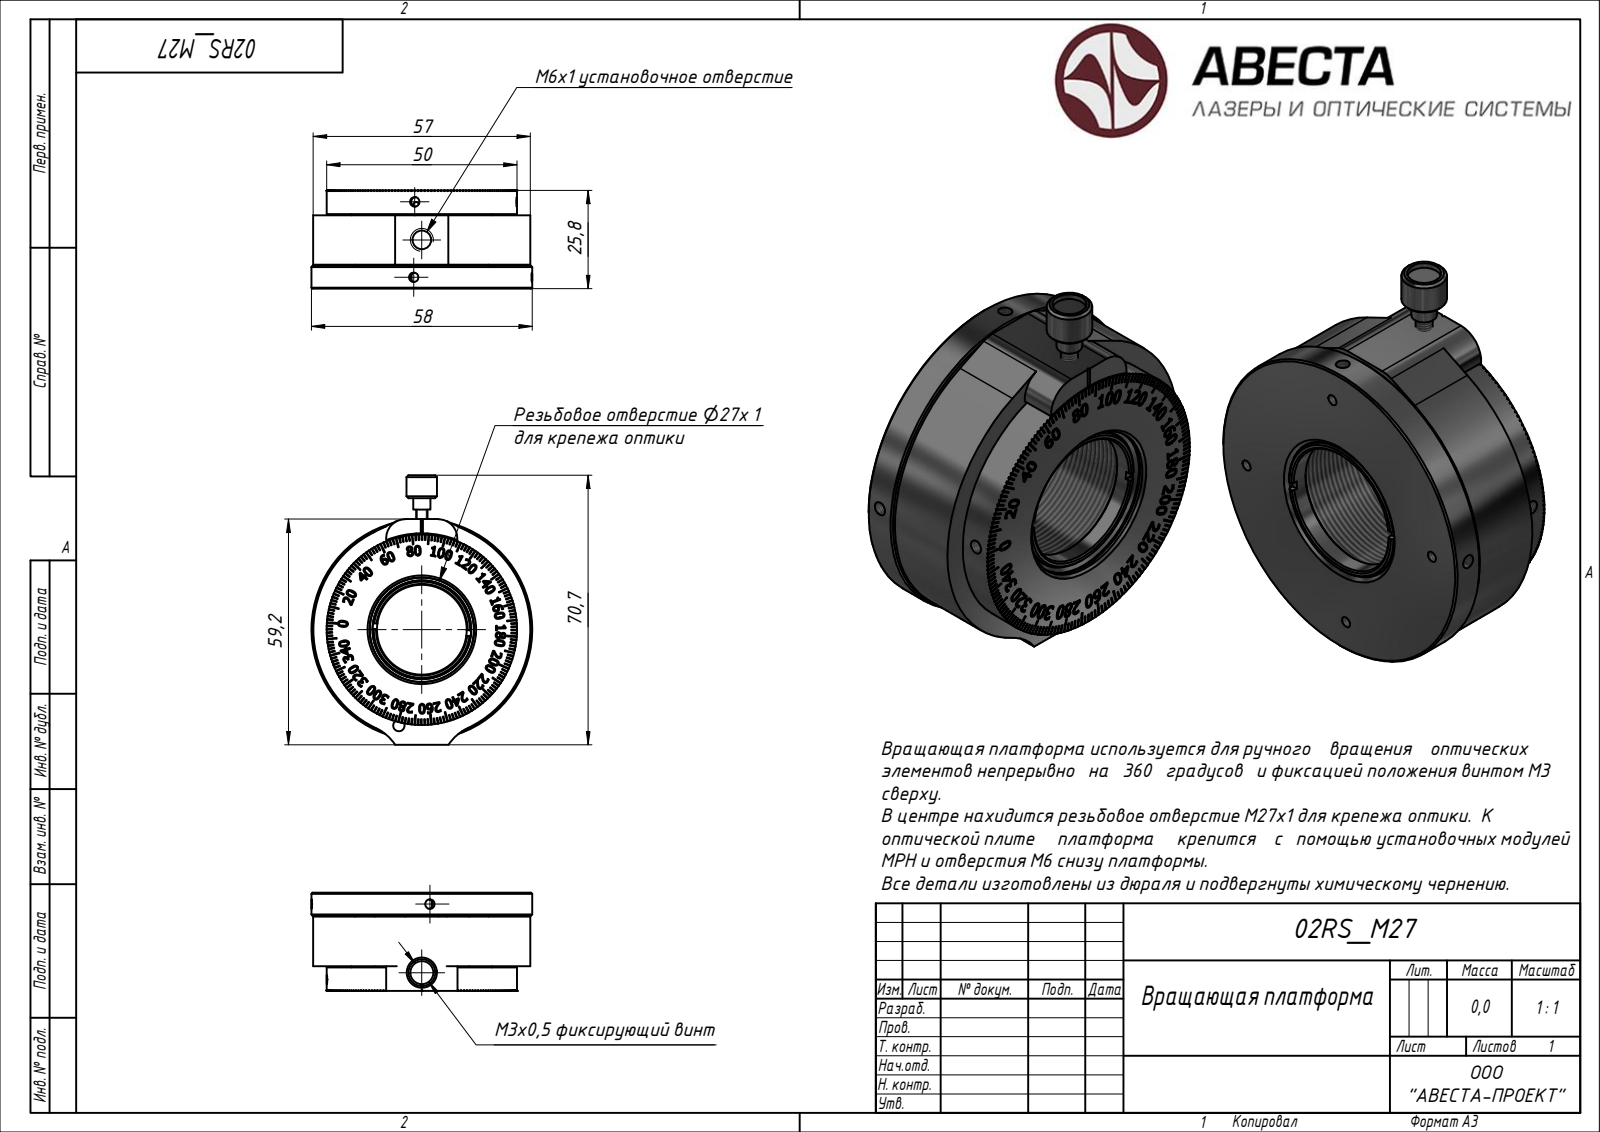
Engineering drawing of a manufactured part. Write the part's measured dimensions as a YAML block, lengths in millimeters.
part_name: "Block 01"
step_written_by: "ST-DEVELOPER v15 (AUTOMOTIVE_DESIGN)"
units: millimeters
bodies: {solids: 4, faces: 1814, planar: 0, cylindrical: 0, other: 1814}
overall_size: [70.7, 58, 27.39]
volume: 259
surface_area: 21528
